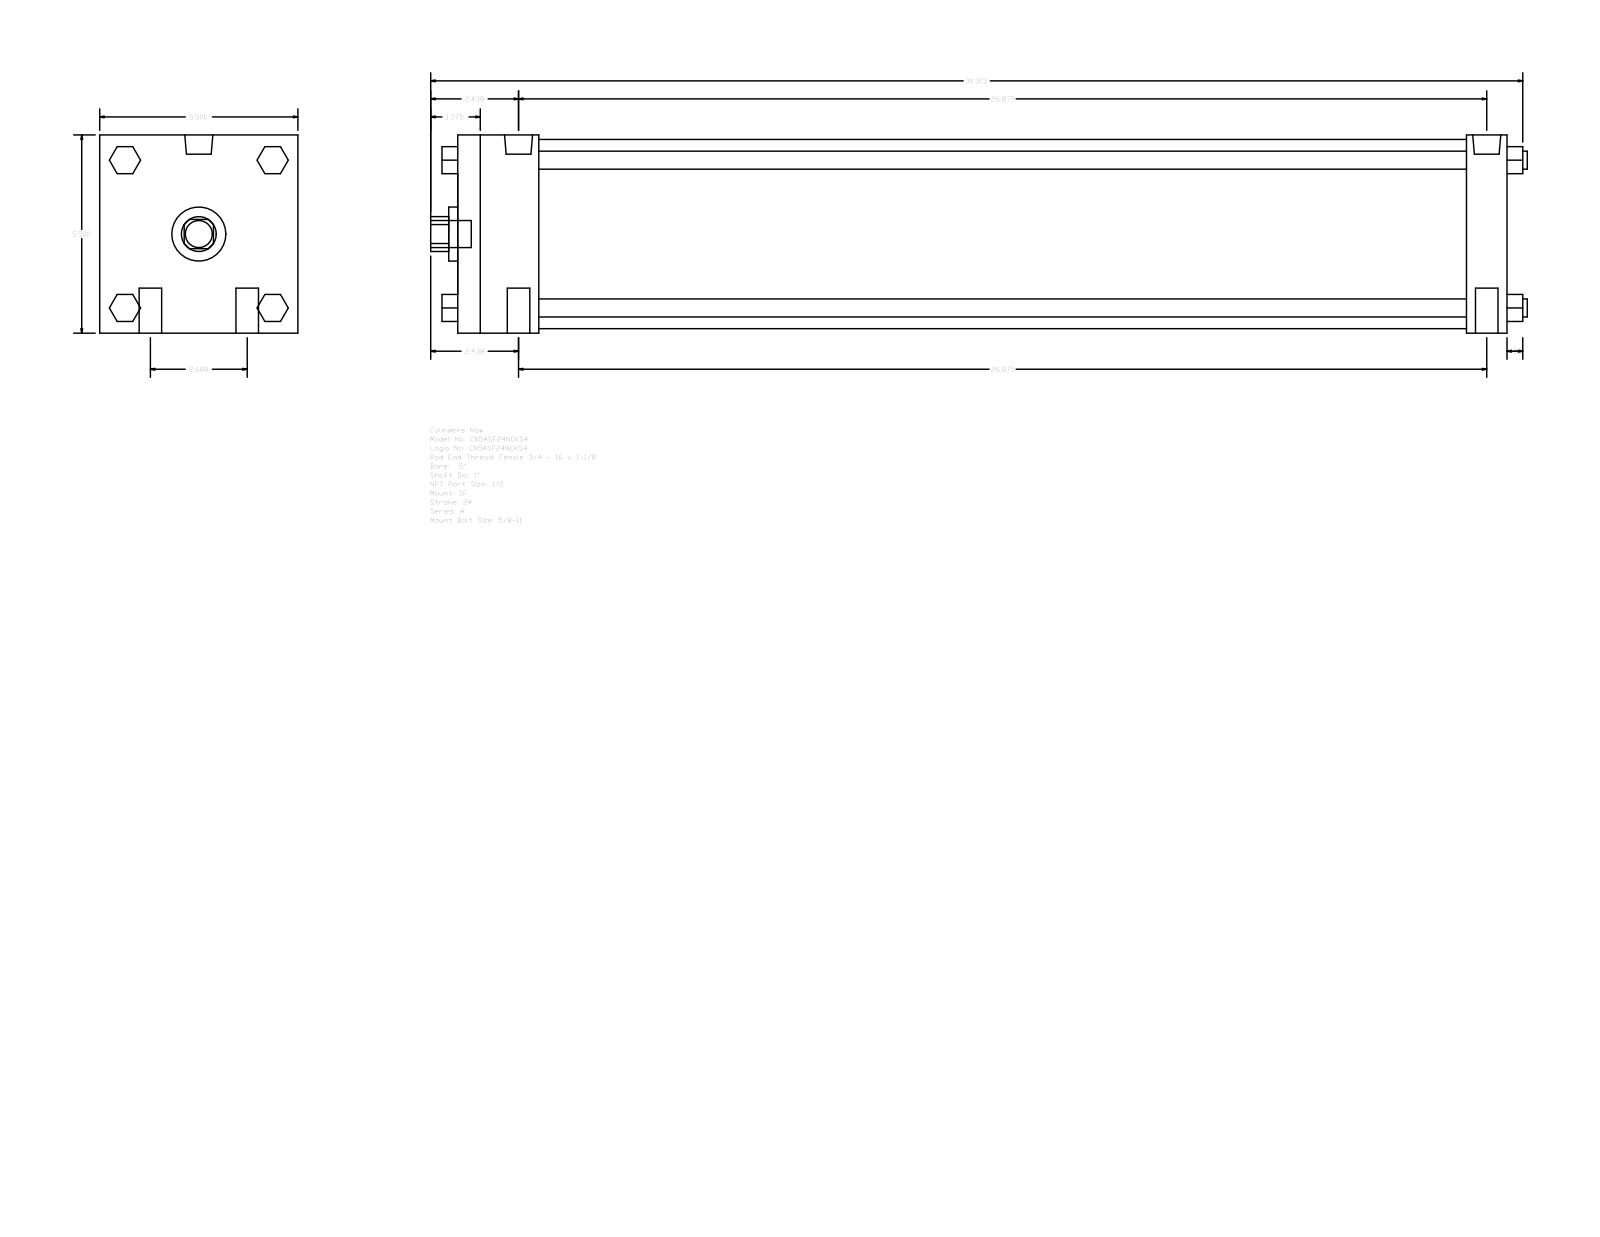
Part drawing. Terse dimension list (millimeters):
name: A_SF__0500_1
written by: GSSL Pune (CONFIG_CONTROL_DESIGN)
unit: mm
bodies: 0 solids, 124 faces (94 planar, 30 cylindrical, 0 other)
size: 773.11 × 139.7 × 139.7
holes: 1× ⌀25.4, 1× ⌀38.1, 1× ⌀133.35
bosses: 4× ⌀15.88, 4× ⌀12.7, 2× ⌀19.77, 2× ⌀8.73, 1× ⌀19.05
rounds: 1× R12.29
face distances: 139.7, 739.78, 57.15, 711.2, 654.05, 682.63, 28.58, 19.05, 52.07, 90.18
